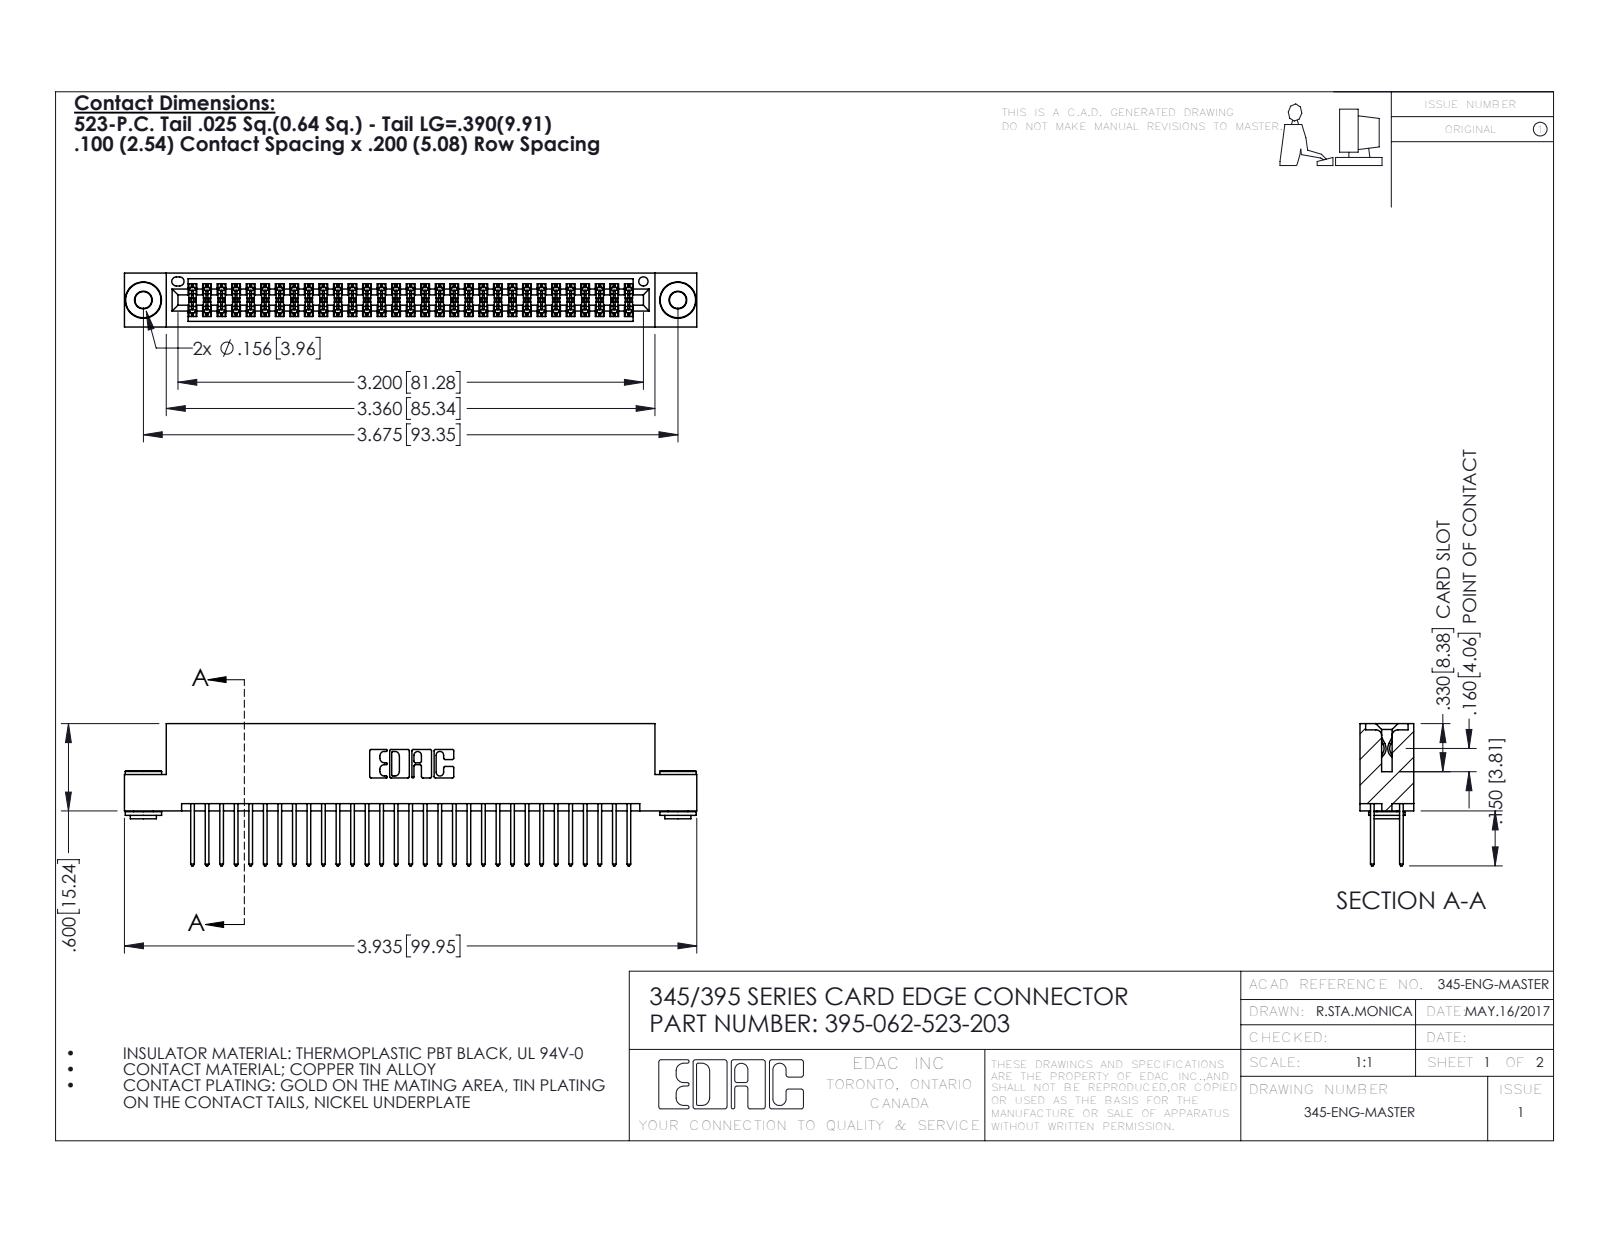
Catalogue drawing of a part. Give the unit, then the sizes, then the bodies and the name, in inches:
Units: inches
Overall size (bounding box): 3.935 × 0.977 × 0.37
Round holes (diameter × count): ⌀0.116 ×2, ⌀0.156 ×2, ⌀0.064 ×1
Round bosses / shafts (diameter × count): ⌀0.25 ×2, ⌀0.18 ×2, ⌀0.136 ×2
Partial cylindrical surfaces — rounded edges, fillets, slot ends (radius × count): R0.006 ×93, R0.01 ×62, R0.01 ×22, R0.007 ×6, R0.031 ×6, R0.026 ×3, R0.014 ×2, R0.019 ×2
Main face-to-face distances: 0.072, 0.298, 0.2, 0.025, 0.098, 0.272, 0.37, 0.225, 0.175, 0.149
Hole centre spacings: 0.27, 3.44, 3.675
Volume: 0.595 in³ · Surface area: 23.22 in²
Bodies: 65 solids, 3264 faces (2136 planar, 1120 cylindrical, 8 other)
Part name (STEP PRODUCT): 345-250-002_345-250-002-102; 345 Part_Flush Mounting Lugs - 0.156 Dia-TH; 345-292-001_345-293-123; 395-062-523-203
STEP written by: SolidWorks 2016 (CONFIG_CONTROL_DESIGN)
